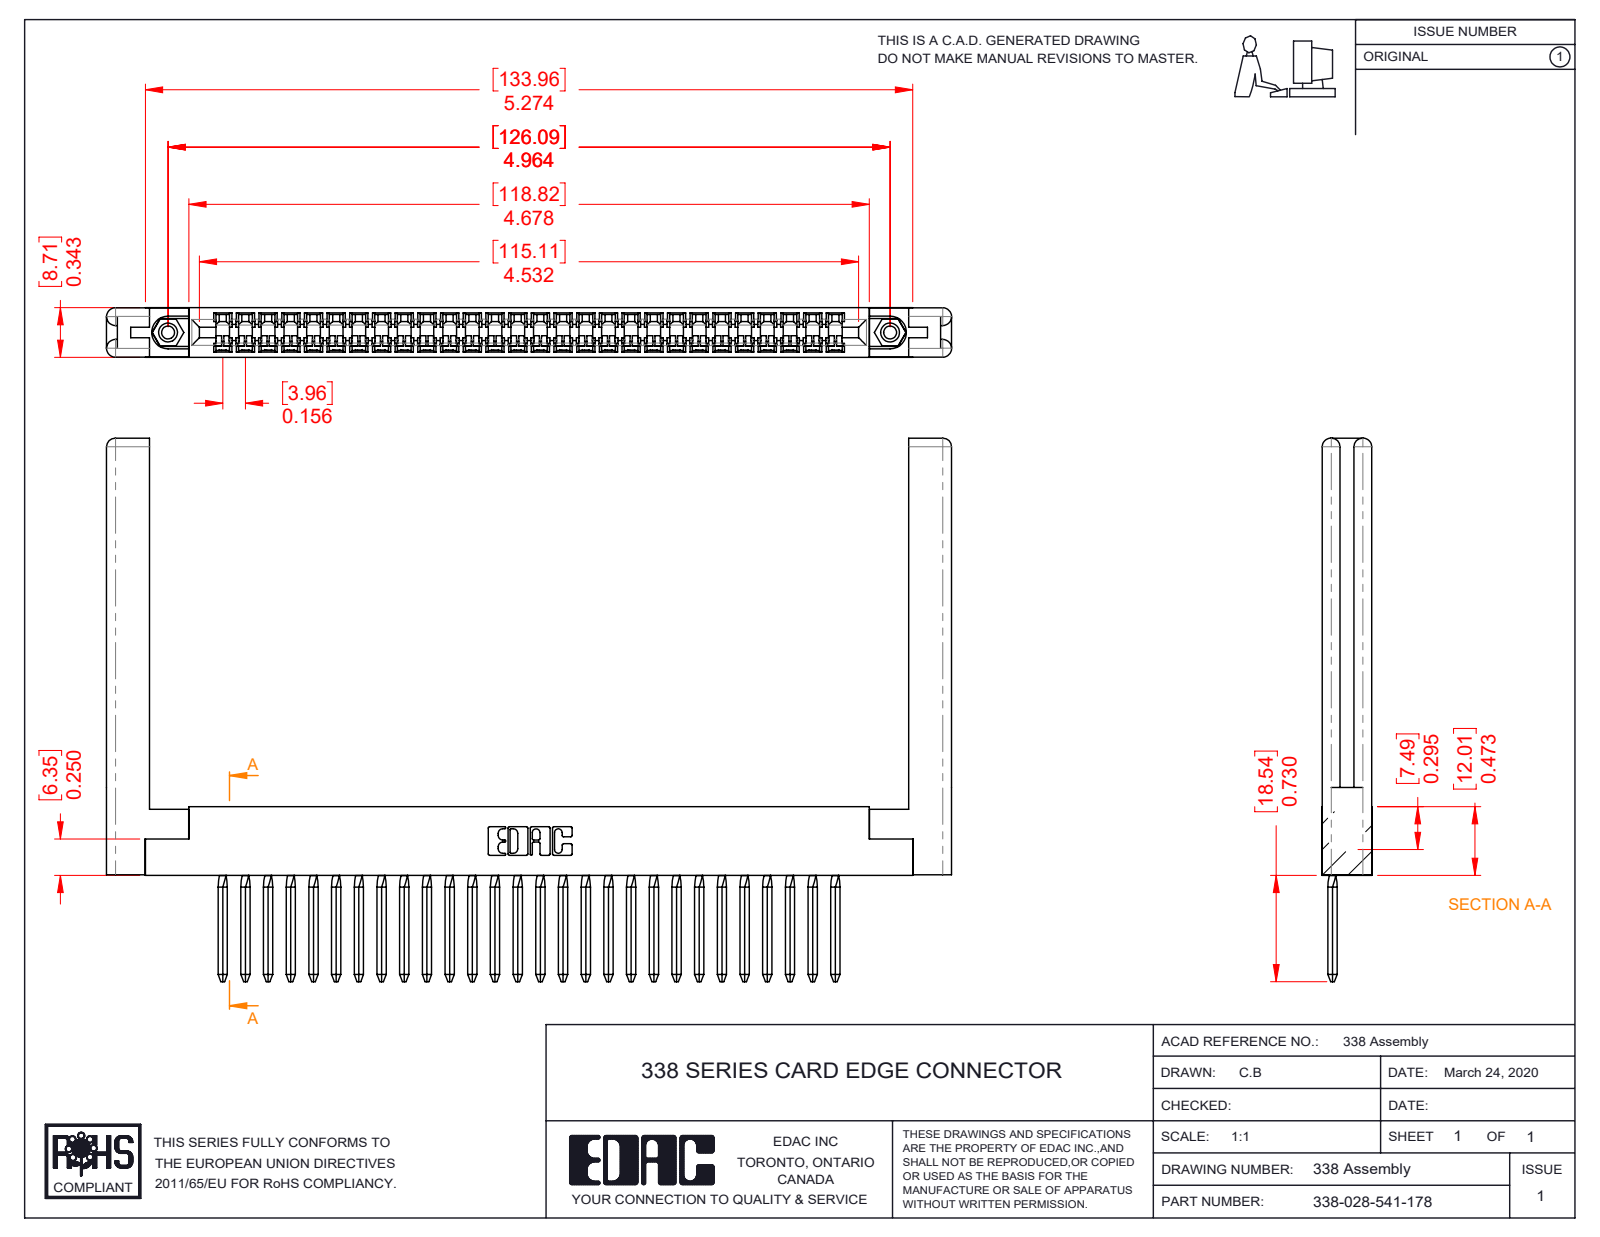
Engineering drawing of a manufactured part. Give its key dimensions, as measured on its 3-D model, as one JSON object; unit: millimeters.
{"part_name": "338-290-001_541; 338-028-541-178; 307-220-058; 338-210-001_338-210-028-004 (+1 more)", "step_written_by": "SolidWorks 2016 (CONFIG_CONTROL_DESIGN)", "units": "millimeters", "bodies": {"solids": 33, "faces": 2840, "planar": 1954, "cylindrical": 750, "other": 136}, "overall_size": [147.6, 94.9, 8.7], "volume_mm3": 17980, "surface_area_mm2": 22060, "round_holes": [[2.3, 2], [3.2, 2], [4, 2]], "round_bosses_or_shafts": [[3.9, 2]], "partial_cylinders_radius": [[0.6, 114], [0.2, 28], [1.4, 23], [1.7, 23], [0.3, 22], [2.5, 22], [1.5, 8], [0.2, 6]], "face_to_face_distances": [8.7, 8.7, 8.6, 3.5, 5.3, 3.4, 5.2, 5.6, 2.3, 7.5], "hole_center_spacings": [126.1]}
